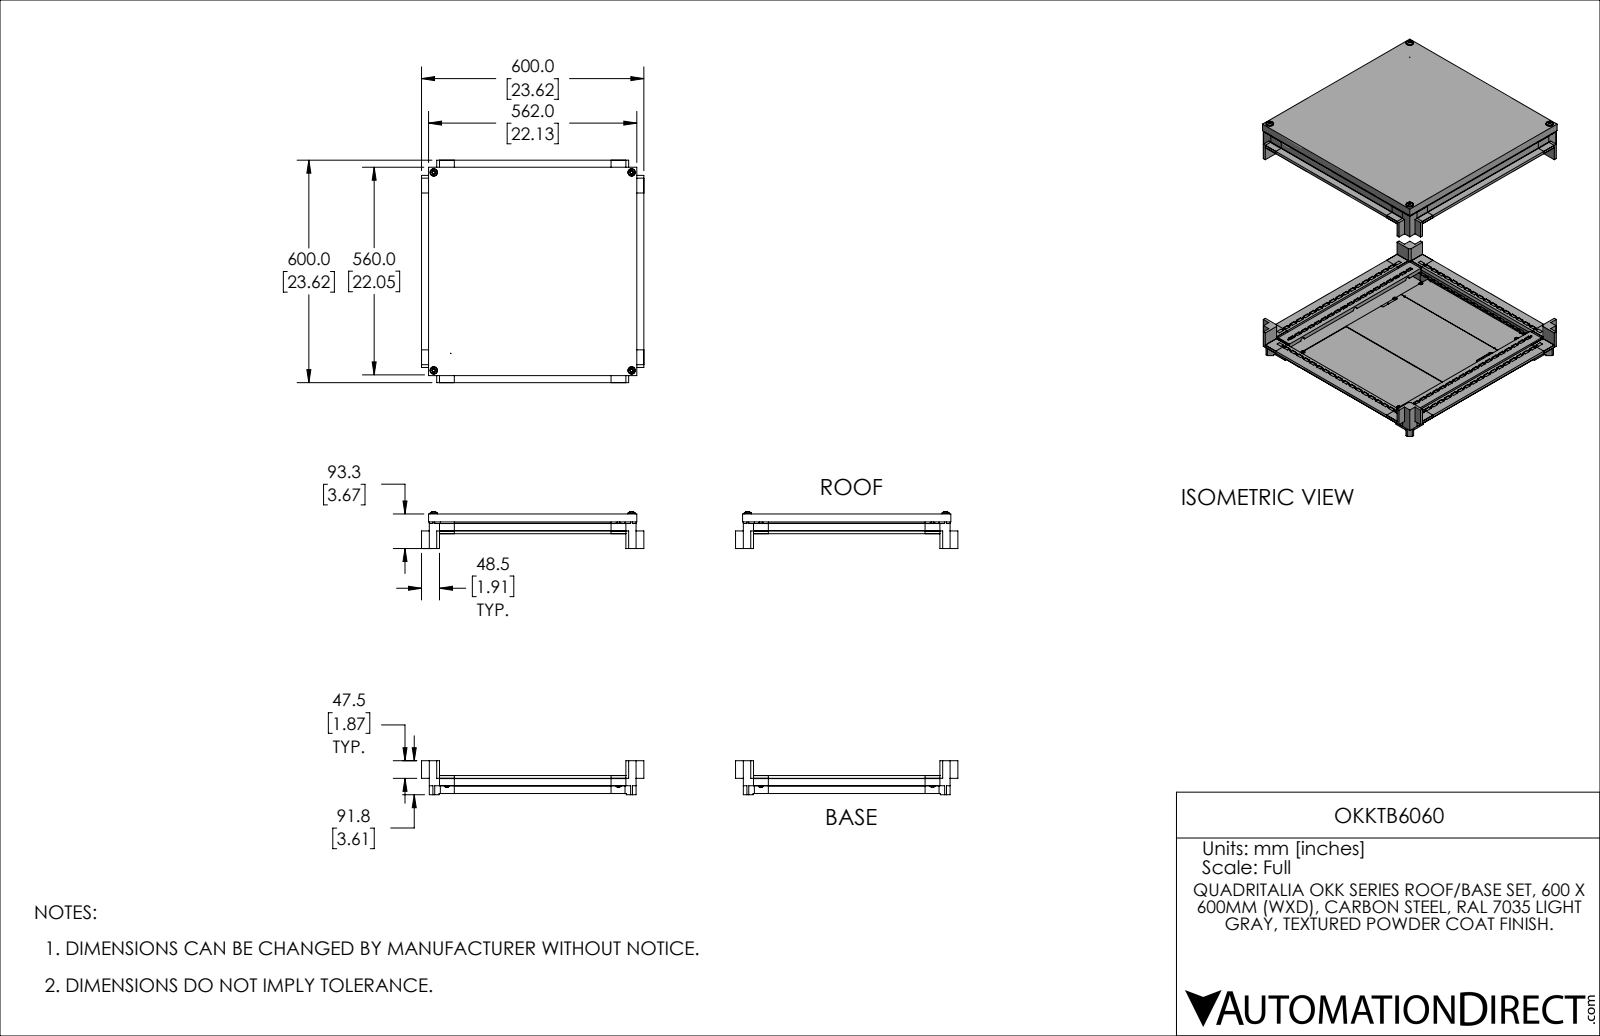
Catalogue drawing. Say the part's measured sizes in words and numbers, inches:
The part is named "OKKTB6060". Its 3-D file was written by "SolidWorks 2021 (AUTOMOTIVE_DESIGN)". It is 59 solids with 4192 faces: 3162 planar, 871 cylindrical and 159 other. Overall it measures 30.057 by 23.622 by 23.622 inches. Its volume is 423.3 cubic inches and its surface area 4 074 square inches. Round holes: 220 of diameter 0.167, 11 of diameter 0.354, 8 of diameter 0.154, 4 of diameter 0.531, 3 of diameter 0.194, 3 of diameter 0.323, 1 of diameter 0.039. Round bosses or shafts: 11 of diameter 0.551, 11 of diameter 0.315, 9 of diameter 0.394, 6 of diameter 0.197, 4 of diameter 0.787, 4 of diameter 0.472, 4 of diameter 0.236, 1 of diameter 0.276. Partial cylindrical surfaces (rounded edges, fillets, slot ends): 264 of radius 0.02, 24 of radius 0.039, 17 of radius 0.03, 16 of radius 0.01, 12 of radius 0.177, 8 of radius 0.138, 6 of radius 0.217, 3 of radius 0.276. The main face-to-face distances are 0.059, 28.759, 28.818, 0.787, 0.098, 1.083, 0.295, 0.689, 0.807, 0.984. The hole center spacings are 0.984, 1.969, 2.953, 3.937, 4.921, 5.906, 6.89, 27.074.
